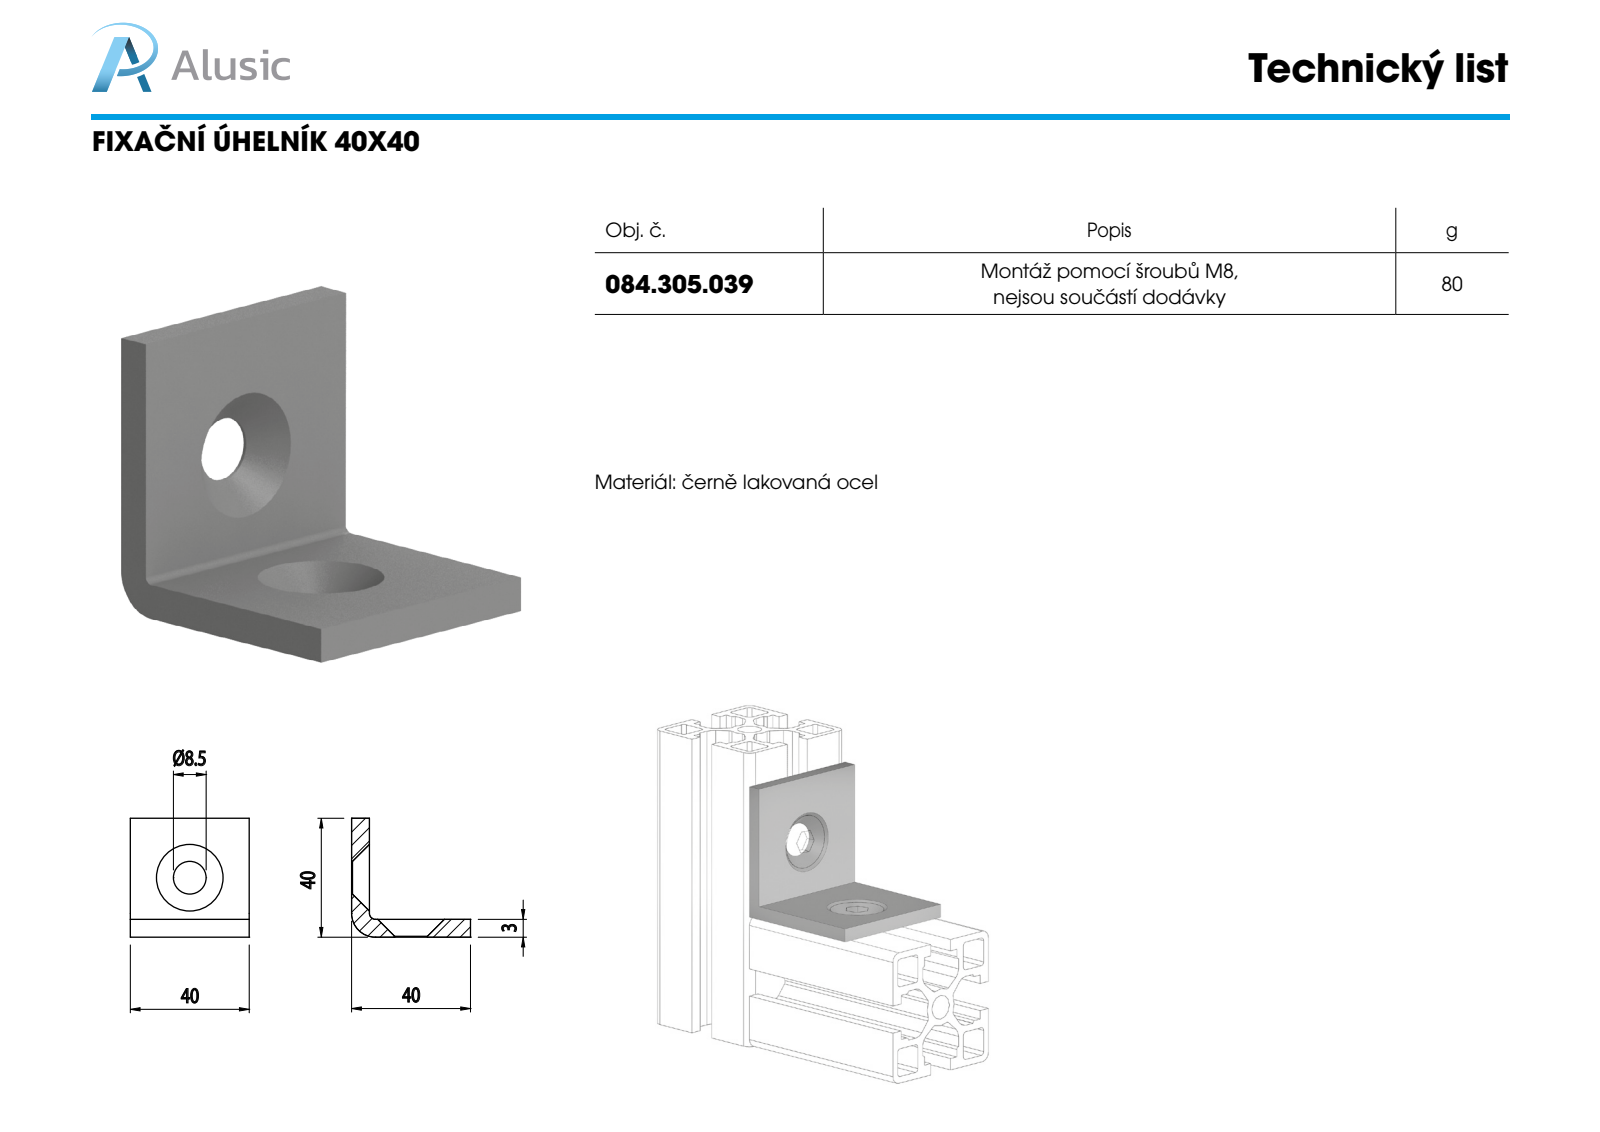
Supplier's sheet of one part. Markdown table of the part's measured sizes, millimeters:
| quantity | value |
| --- | --- |
| part name | 084.305.039 |
| STEP written by | SolidWorks 2012 (CONFIG_CONTROL_DESIGN) |
| units | millimeters |
| bodies | 1 solid, 16 faces (8 planar, 4 cylindrical, 4 other) |
| overall size | 40 × 40 × 40 |
| volume | 13 616 mm³ |
| surface area | 7 082 mm² |
| round holes (diameter × count) | 9 × 2 |
| main face-to-face distances | 5, 40, 35 |
